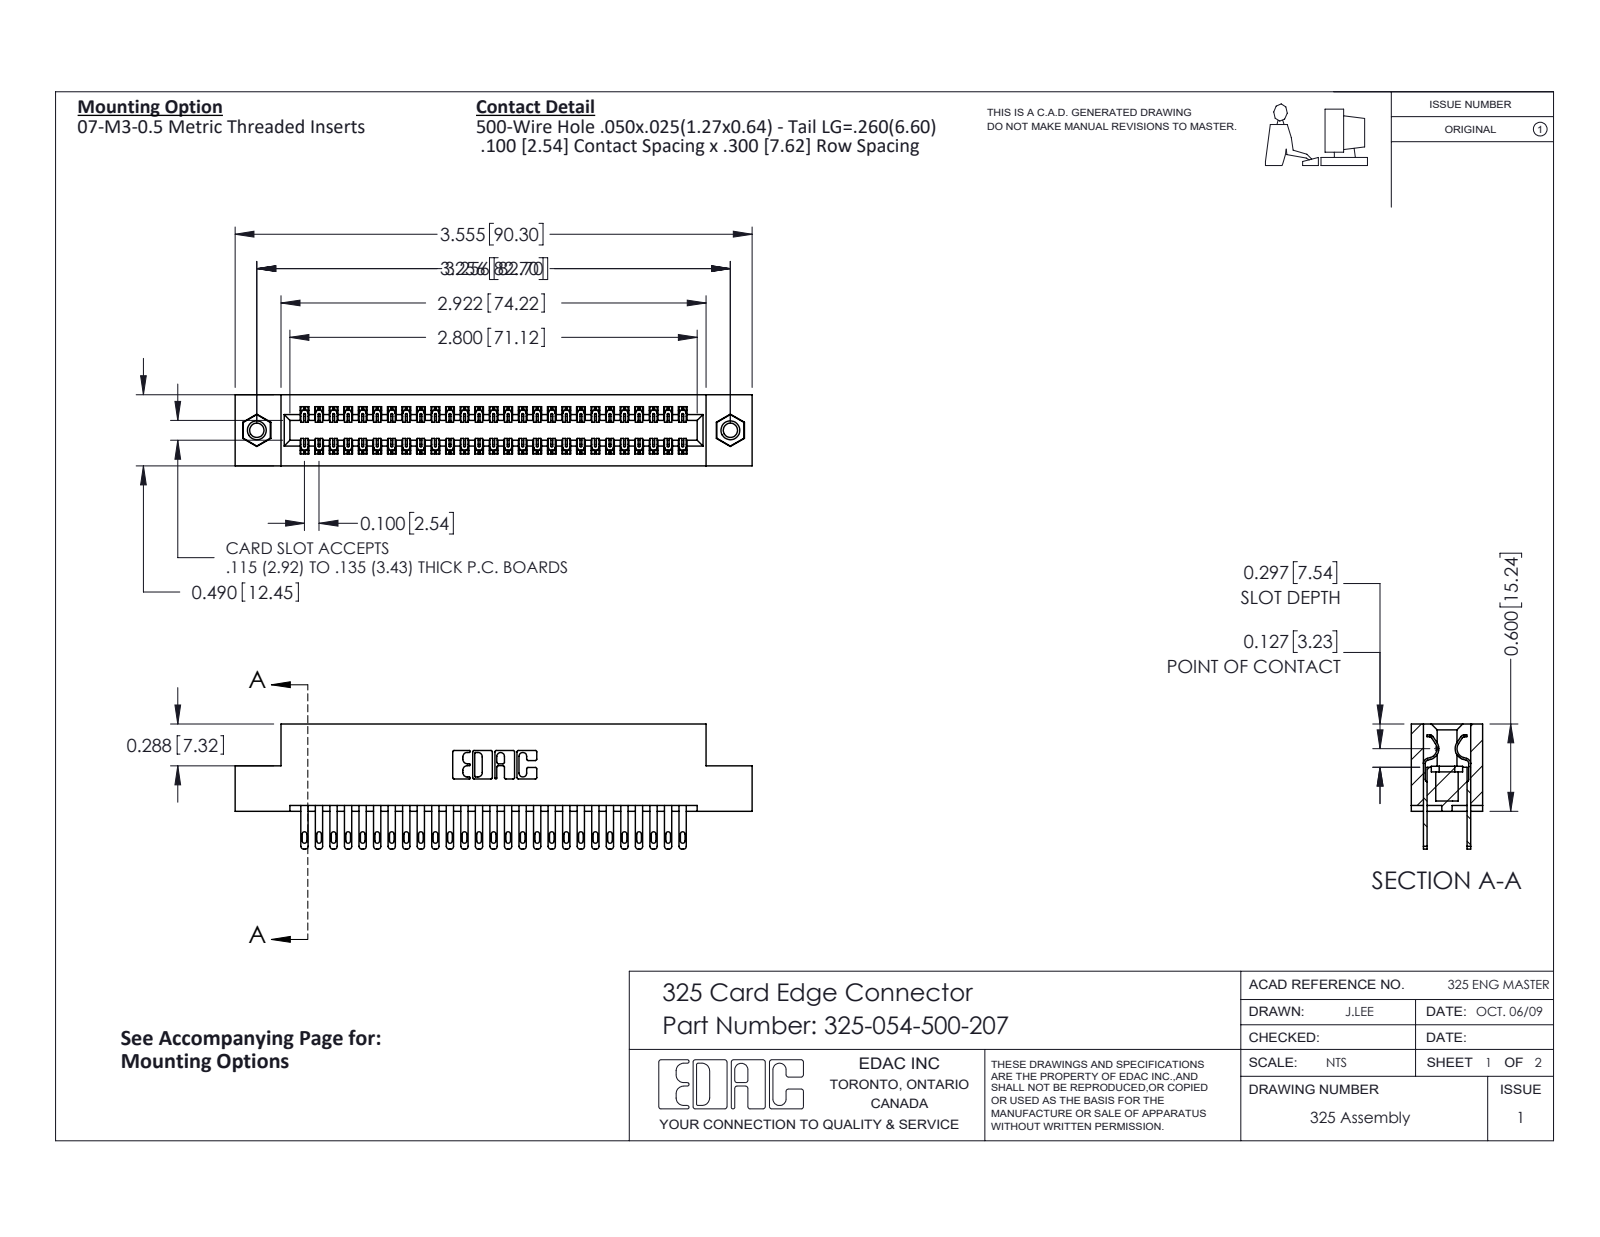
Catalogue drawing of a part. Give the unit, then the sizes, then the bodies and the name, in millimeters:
Units: millimetres
Overall size (bounding box): 90.3 × 21.8 × 12.4
Round holes (diameter × count): ⌀2.5 ×2, ⌀3.2 ×2, ⌀4.1 ×2
Round bosses / shafts (diameter × count): ⌀3.9 ×2
Partial cylindrical surfaces — rounded edges, fillets, slot ends (radius × count): R0.2 ×81, R0.4 ×54, R0.5 ×54, R0.3 ×22, R0.2 ×6, R0.8 ×6, R0.7 ×3, R0.4 ×2
Main face-to-face distances: 2.1, 10.3, 7.6, 2.7, 9.7, 0.6, 12.4, 8.3, 7, 1
Hole centre spacings: 82.7
Volume: 11 700 mm³ · Surface area: 14 370 mm²
Bodies: 57 solids, 2766 faces (1722 planar, 1028 cylindrical, 16 other)
Part name (STEP PRODUCT): 325-054-500-207; 345-250-001_345-250-005-103; 325-292-001_325-293-100; 325 Part_TI
STEP written by: SolidWorks 2016 (CONFIG_CONTROL_DESIGN)
